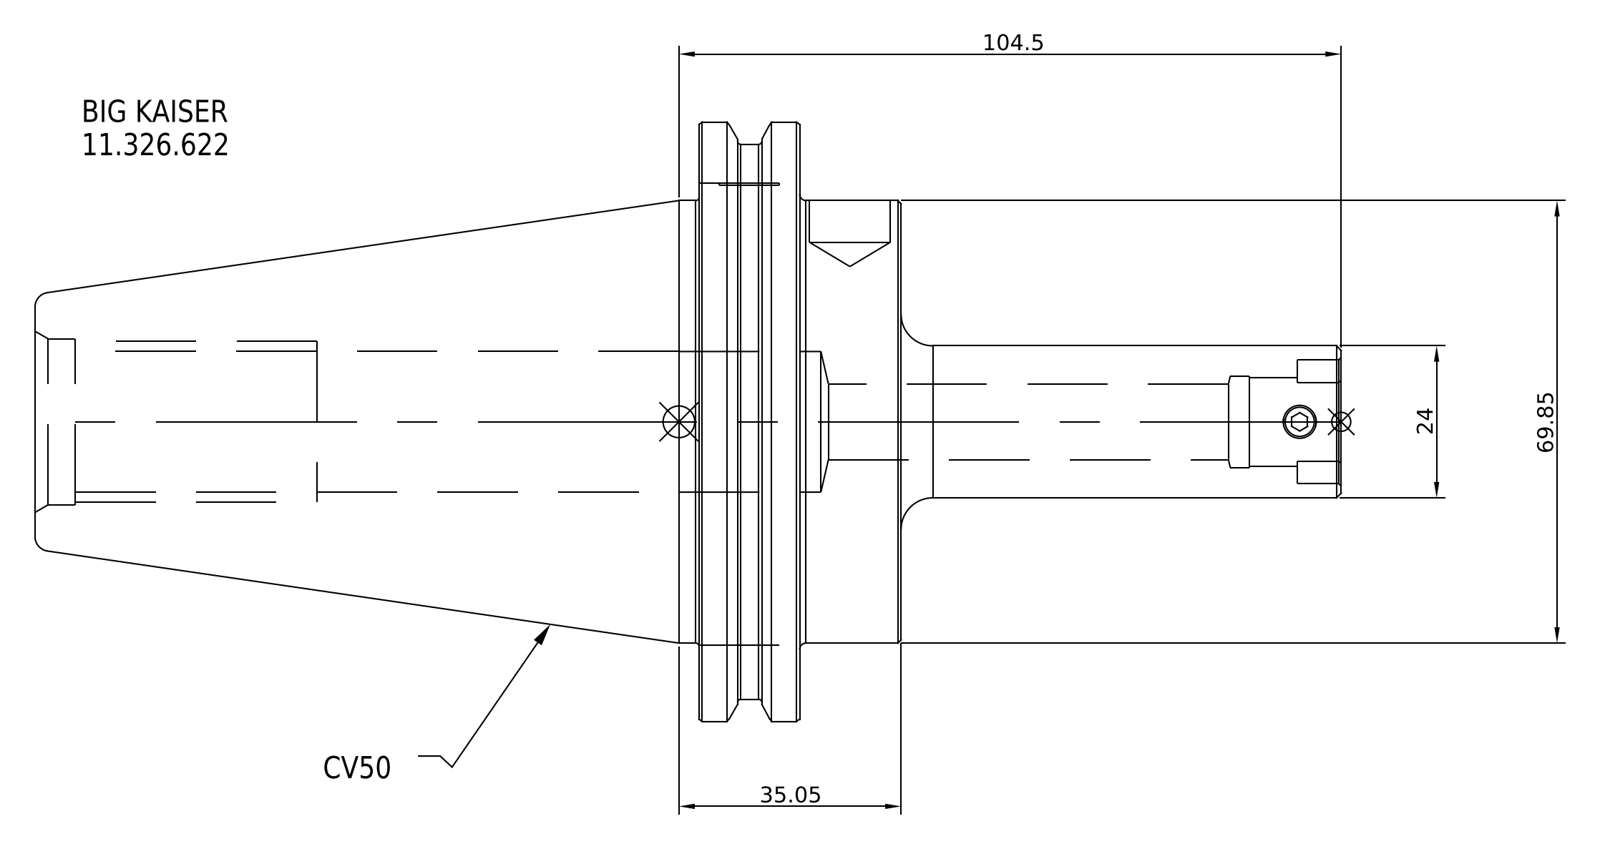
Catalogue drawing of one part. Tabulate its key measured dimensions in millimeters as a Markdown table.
| quantity | value |
| --- | --- |
| part name | 11.326.622 |
| STEP written by | SolidWorks 2021 (CONFIG_CONTROL_DESIGN) |
| units | millimeters |
| bodies | 1 solid, 16 faces (7 planar, 6 cylindrical, 3 other) |
| overall size | 206.1 × 98.43 × 98.43 |
| volume | 473 922 mm³ |
| surface area | 46 213 mm² |
| round bosses / shafts (diameter × count) | 98.43 × 1, 91.29 × 1, 69.85 × 1, 24 × 1 |
| main face-to-face distances | 17.55, 15.95, 33.5, 136.6, 120.65, 103.1, 69.5, 85.45, 103, 206.1 |
